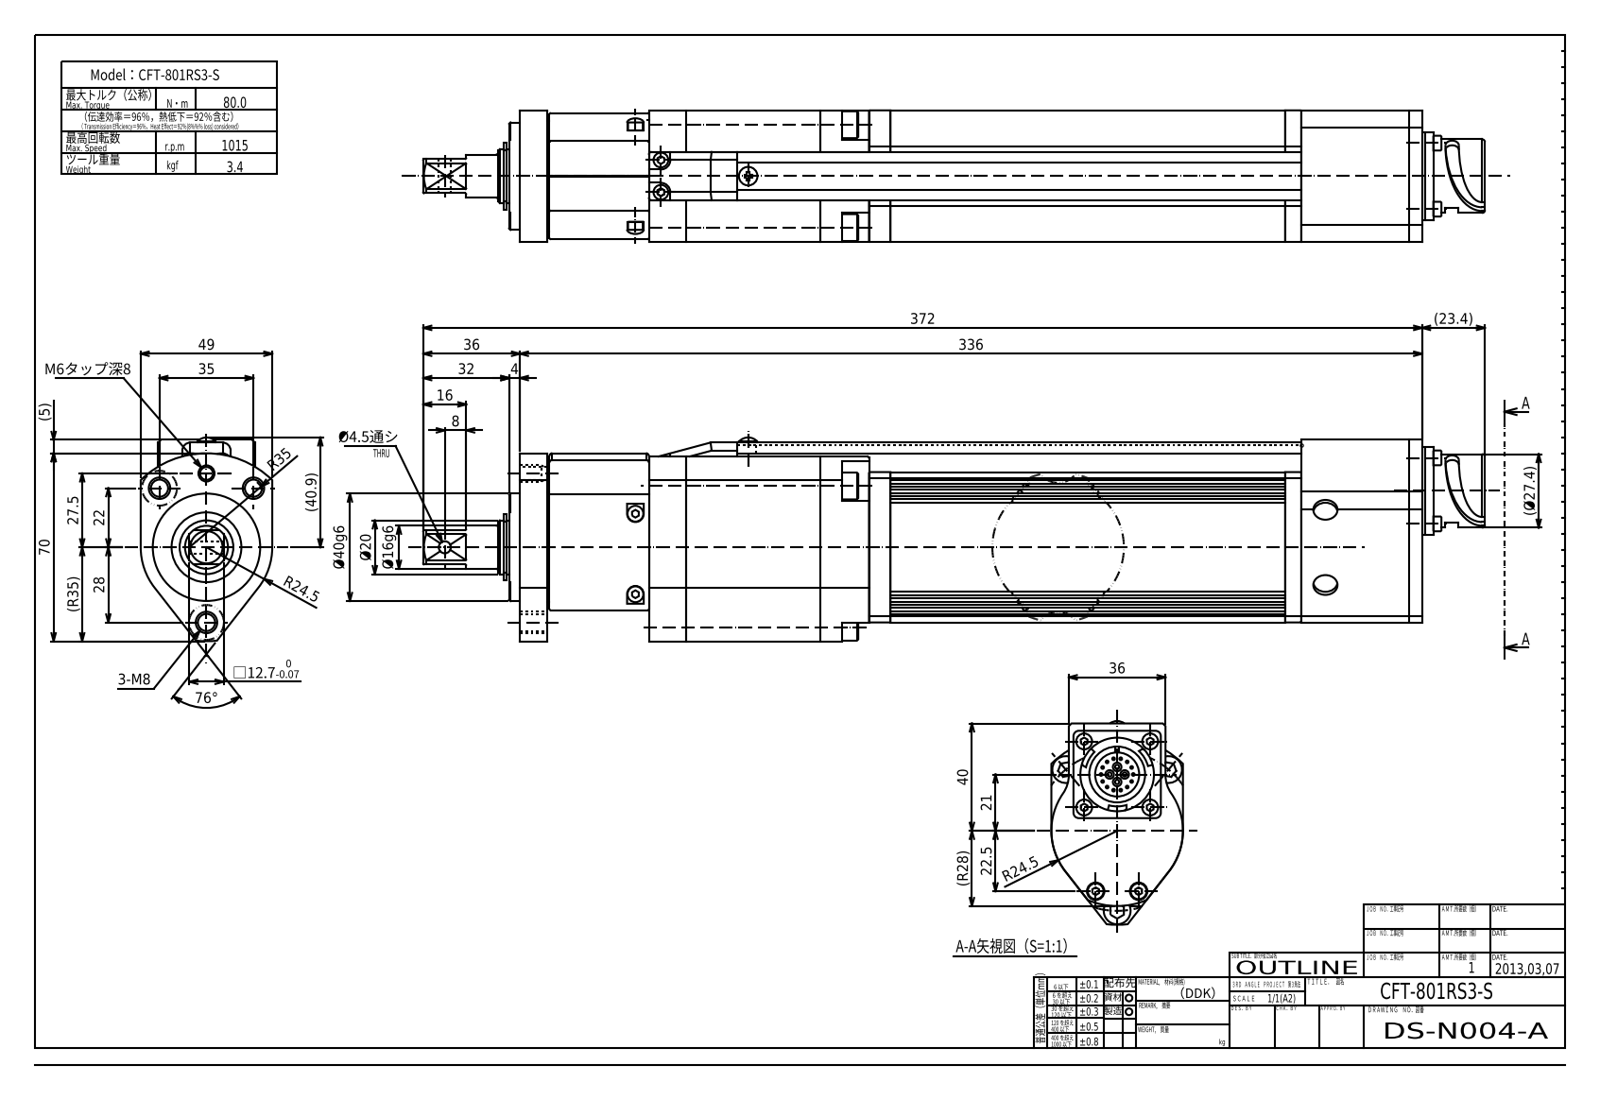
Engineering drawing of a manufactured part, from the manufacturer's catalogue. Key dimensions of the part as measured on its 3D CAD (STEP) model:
Part name (STEP PRODUCT): CFT-801RS3-S
STEP written by: SolidWorks 2013 (CONFIG_CONTROL_DESIGN)
Units: millimetres
Bodies: 18 solids, 315 faces (129 planar, 134 cylindrical, 52 other)
Overall size (bounding box): 394.4 × 77.2 × 49
Volume: 790 248 mm³ · Surface area: 139 609 mm²
Round holes (diameter × count): ⌀6.8 ×3, ⌀4.5 ×1, ⌀5 ×1, ⌀20.8 ×1
Round bosses / shafts (diameter × count): ⌀5.5 ×4, ⌀10 ×3, ⌀8.5 ×3, ⌀47 ×1, ⌀41 ×1, ⌀40 ×1, ⌀27.4 ×1, ⌀20 ×1
Partial cylindrical surfaces — rounded edges, fillets, slot ends (radius × count): R0.5 ×7, R2 ×6, R1 ×4, R3 ×4, R9 ×2, R12 ×2, R24.5 ×1, R28 ×1
Main face-to-face distances: 50, 224, 1, 14, 27, 5, 10, 219, 269, 39
Hole centre spacings: 17.53, 18.34, 52.97, 6.5, 35, 49, 55.5
